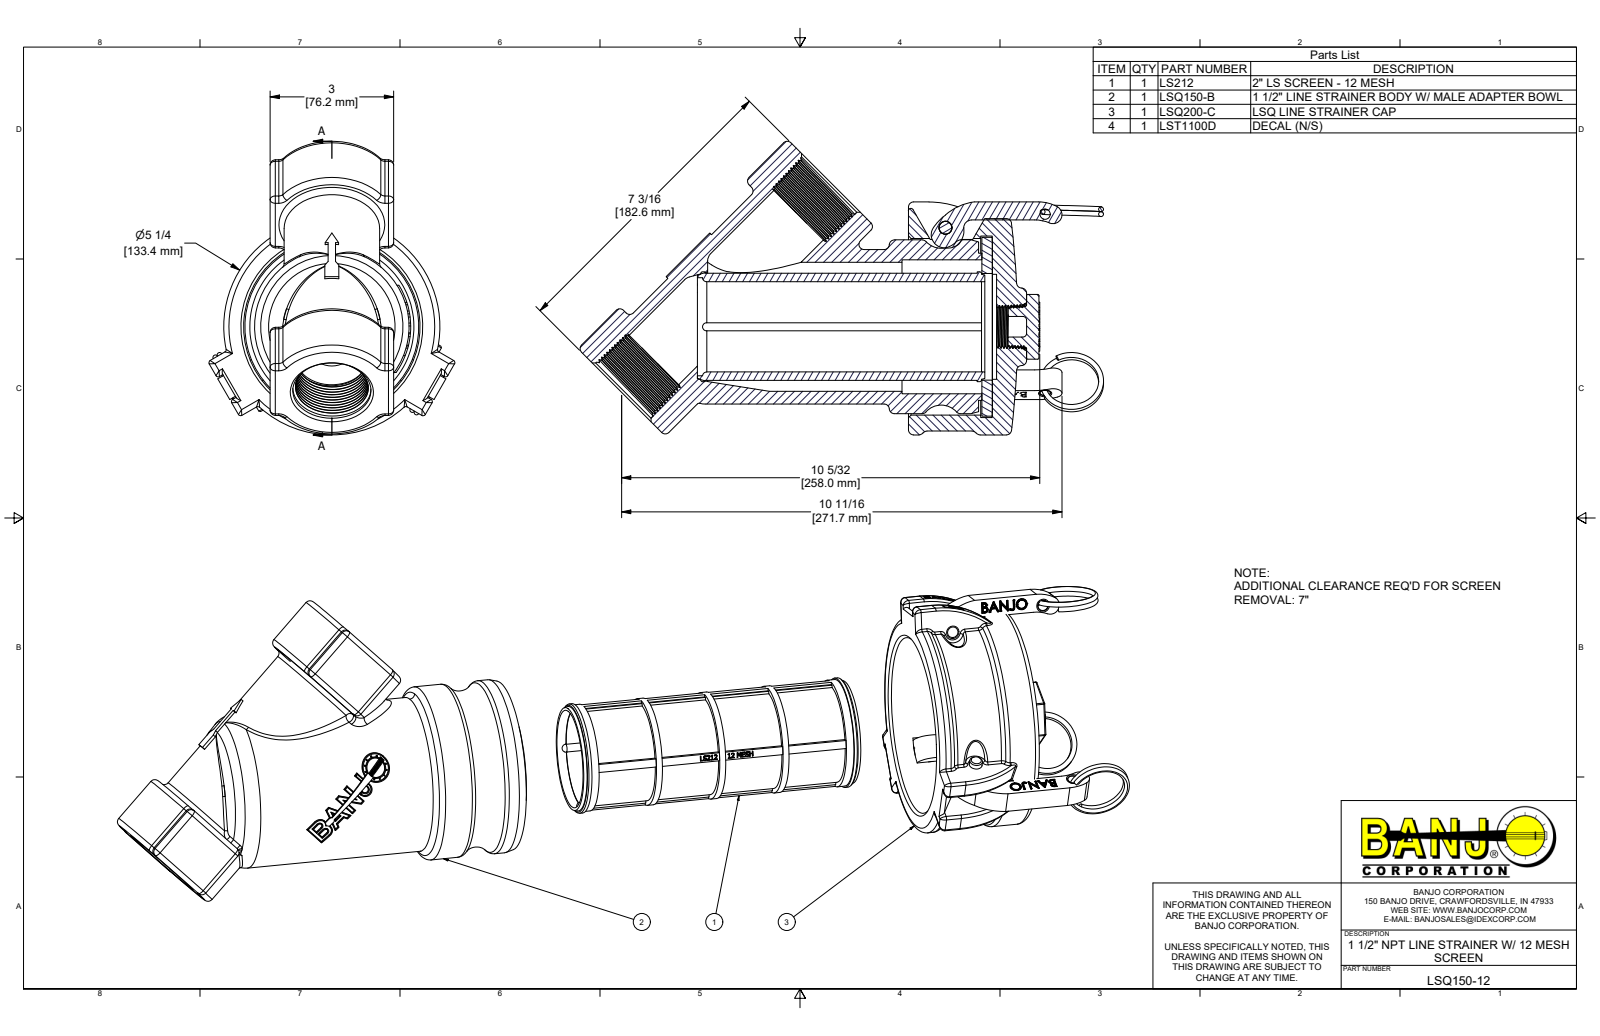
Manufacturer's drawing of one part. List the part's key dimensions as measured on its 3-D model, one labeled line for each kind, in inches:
Part name (STEP PRODUCT): LSQ150-12; LSQ150-B; LSQ200-C; LSQ200-MYC (+8 more)
STEP written by: Autodesk Inventor 2019 (AUTOMOTIVE_DESIGN)
Units: inches
Bodies: 15 solids, 3438 faces (1206 planar, 828 cylindrical, 1404 other)
Overall size (bounding box): 19.064 × 7.127 × 5.974
Volume: 78.9 in³ · Surface area: 630.6 in²
Round holes (diameter × count): ⌀0.25 ×3, ⌀0.312 ×3, ⌀0.319 ×3, ⌀1.7 ×2, ⌀0.454 ×1, ⌀0.5 ×1, ⌀0.641 ×1, ⌀2.19 ×1, ⌀2.35 ×1, ⌀2.55 ×1, ⌀2.59 ×1, ⌀3.13 ×1
Round bosses / shafts (diameter × count): ⌀0.325 ×3, ⌀0.311 ×3, ⌀5.25 ×1, ⌀4.34 ×1, ⌀4.22 ×1, ⌀3.75 ×1, ⌀3.57 ×1, ⌀2.666 ×1
Partial cylindrical surfaces — rounded edges, fillets, slot ends (radius × count): R0.006 ×353, R0.005 ×51, R0.125 ×47, R0.06 ×27, R0.03 ×18, R0.929 ×6, R0.25 ×5, R0.1 ×4
Main face-to-face distances: 0.25, 0.255, 2.04, 2.035, 1.785, 0.45, 0.61, 0.1, 0.355, 0.03
Hole centre spacings: 2.442, 3.359, 5.685
